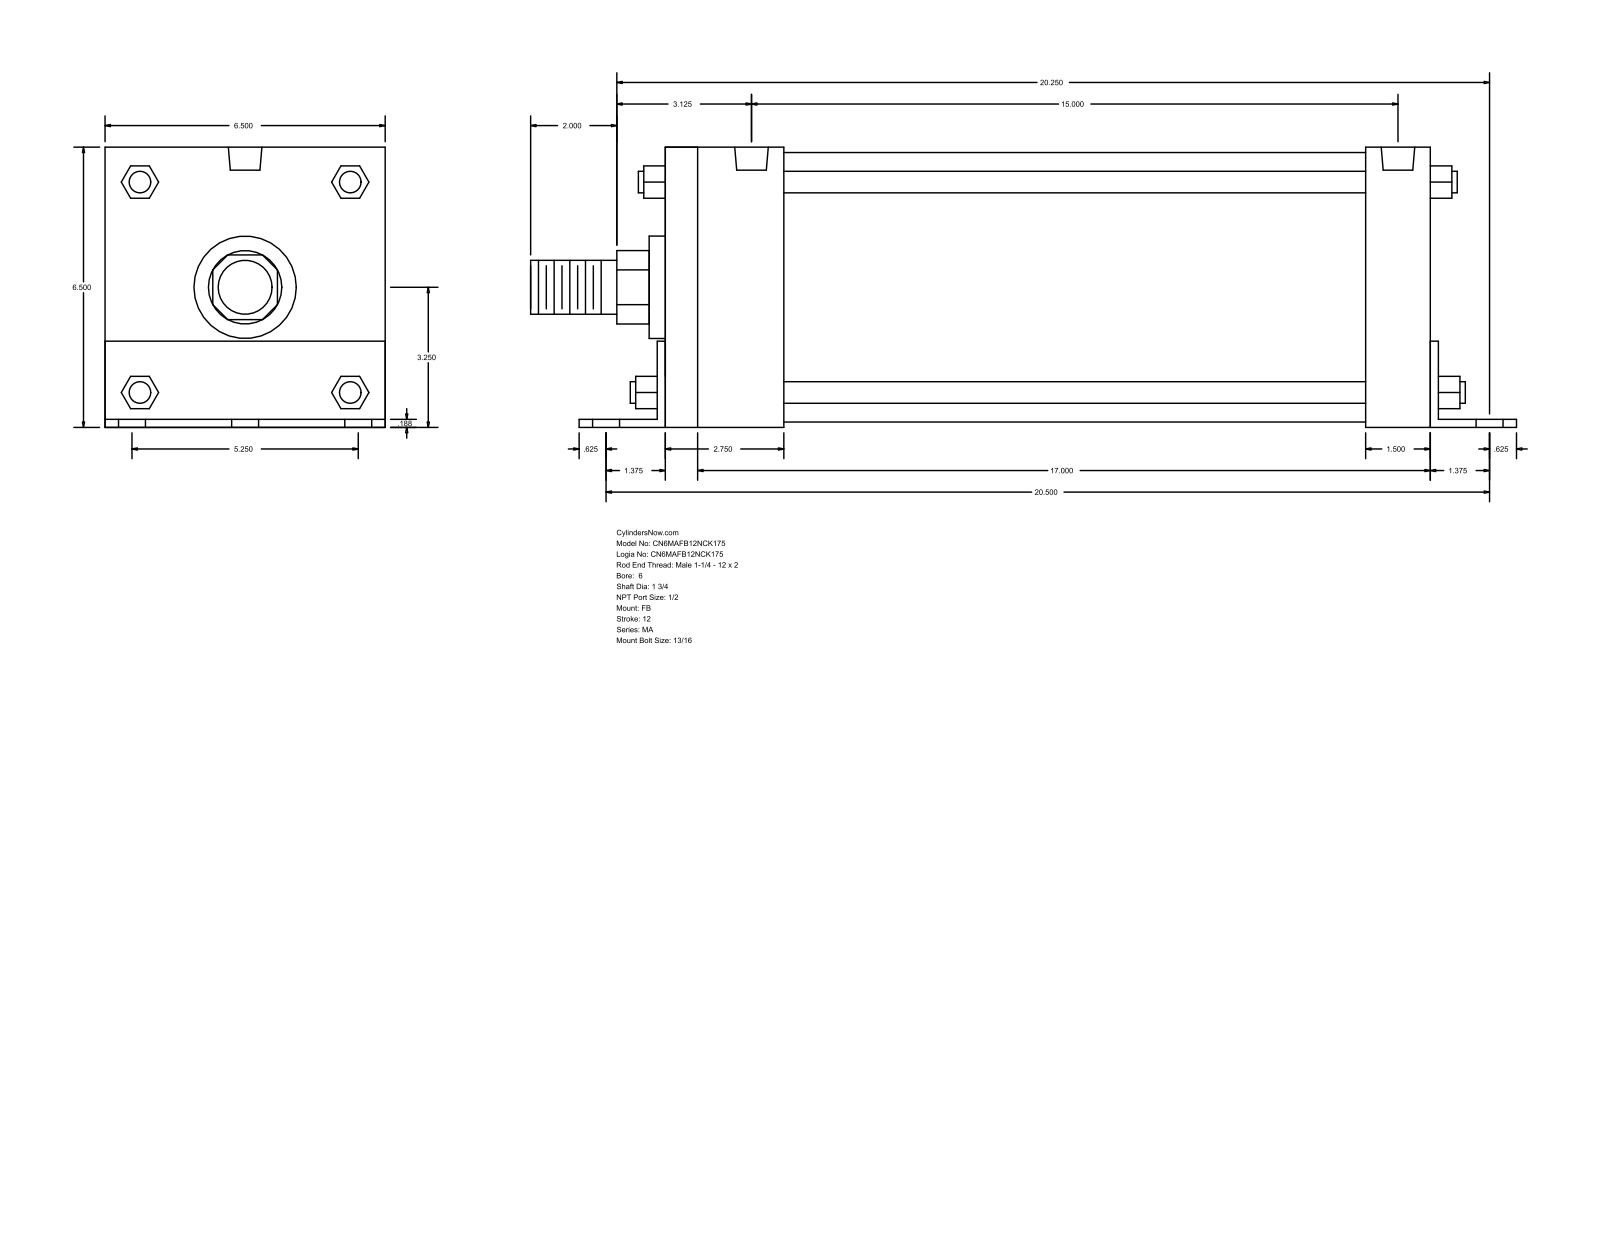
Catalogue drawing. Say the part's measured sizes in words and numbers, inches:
The part is named "MA_FB__0600_1.75". Its 3-D file was written by "GSSL Pune (CONFIG_CONTROL_DESIGN)". It is 0 solids with 140 faces: 105 planar, 35 cylindrical and 0 other. Overall it measures 22.875 by 6.502 by 6.5 inches. Round holes: 6 of diameter 0.813, 4 of diameter 0.687, 2 of diameter 0.778. Round bosses or shafts: 4 of diameter 0.5, 1 of diameter 6.25, 1 of diameter 2.375, 1 of diameter 1.75, 1 of diameter 1.25. Partial cylindrical surfaces (rounded edges, fillets, slot ends): 1 of radius 0.852, 1 of radius 1.262. The main face-to-face distances are 6.5, 0.187, 17.75, 6.502, 17.938, 0.185, 6.315, 18.125, 1.5, 2.75. The hole center spacings are 2.625, 20.667, 20.5, 3.377, 4.276, 5.25, 15, 17.325.
